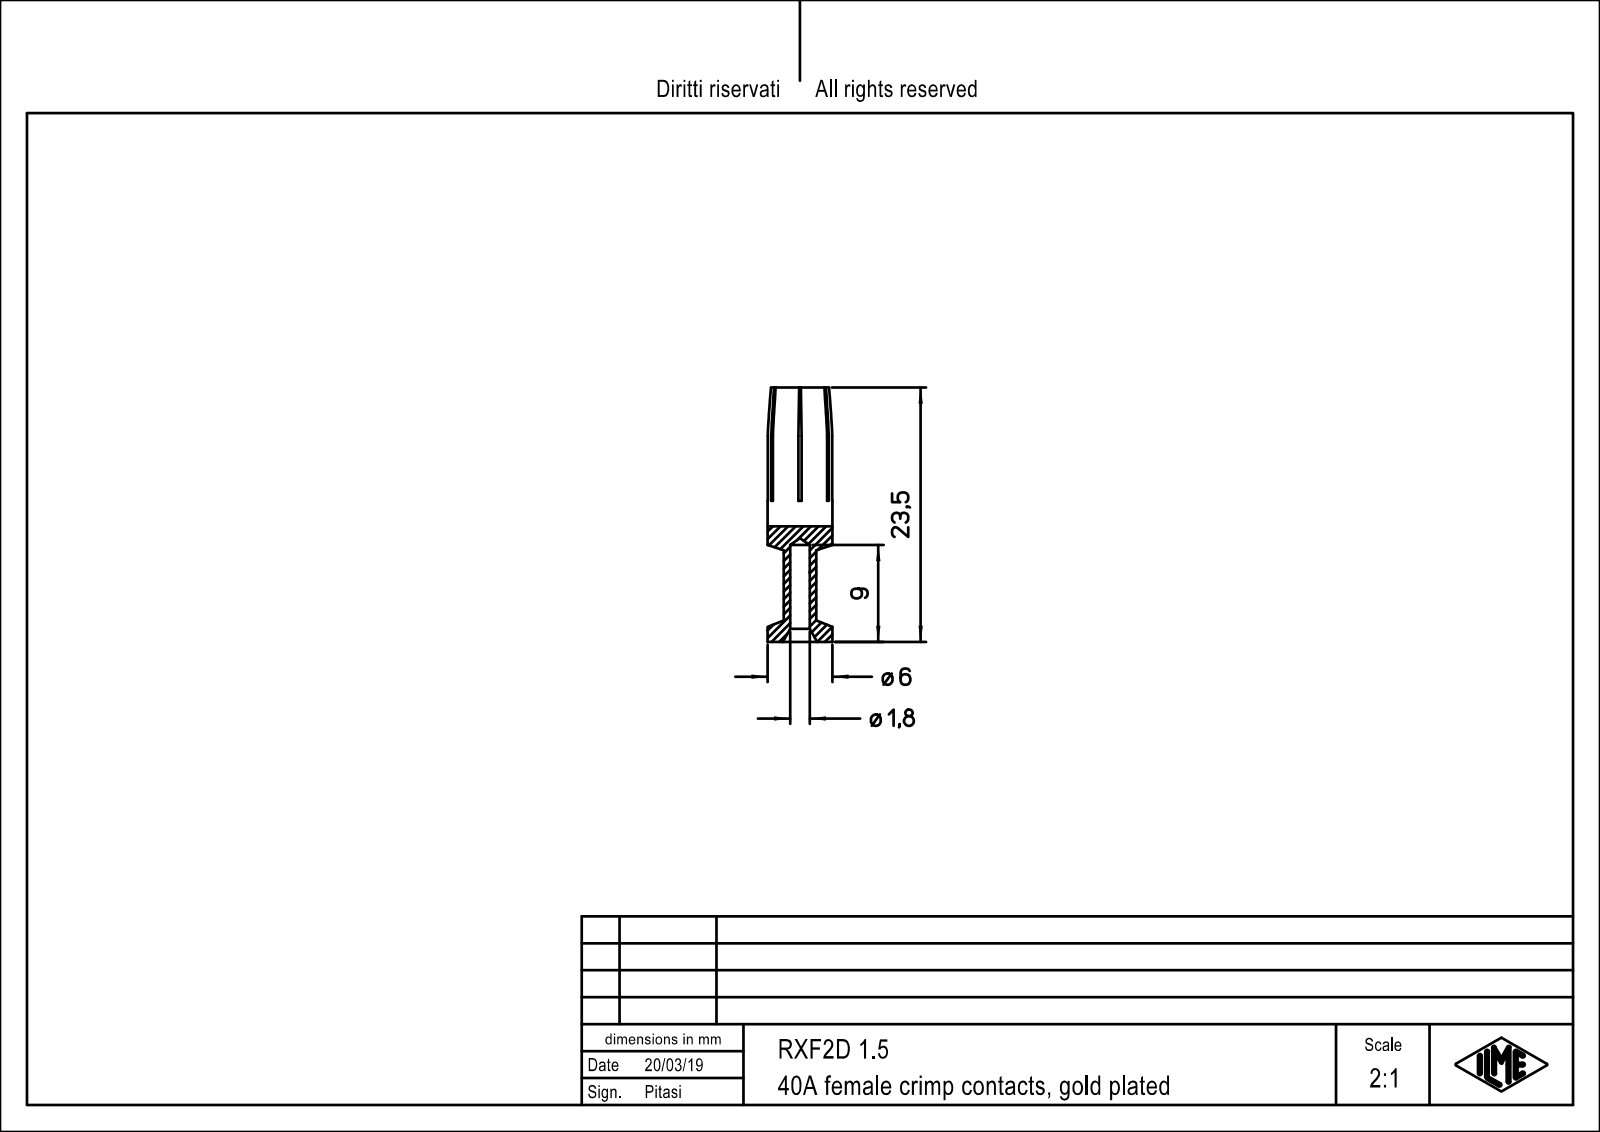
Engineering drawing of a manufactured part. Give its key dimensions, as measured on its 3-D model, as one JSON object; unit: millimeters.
{"part_name": "RXF2D_1-5", "step_written_by": "PTC Creo Elements/Direct Modeling 19.0E 27-Jun-2016 (C) Parametric Technology GmbH (AUTOMOTIVE_DESIGN)", "units": "millimeters", "bodies": {"solids": 1, "faces": 108, "planar": 58, "cylindrical": 14, "other": 36}, "overall_size": [23.5, 6, 6], "volume_mm3": 330, "surface_area_mm2": 724, "round_holes": [[1.8, 1], [4.2, 1]], "round_bosses_or_shafts": [[6, 1], [3, 1]], "face_to_face_distances": [0.47, 13, 23.5, 10.5, 8, 5, 15.5, 9, 1, 4]}
